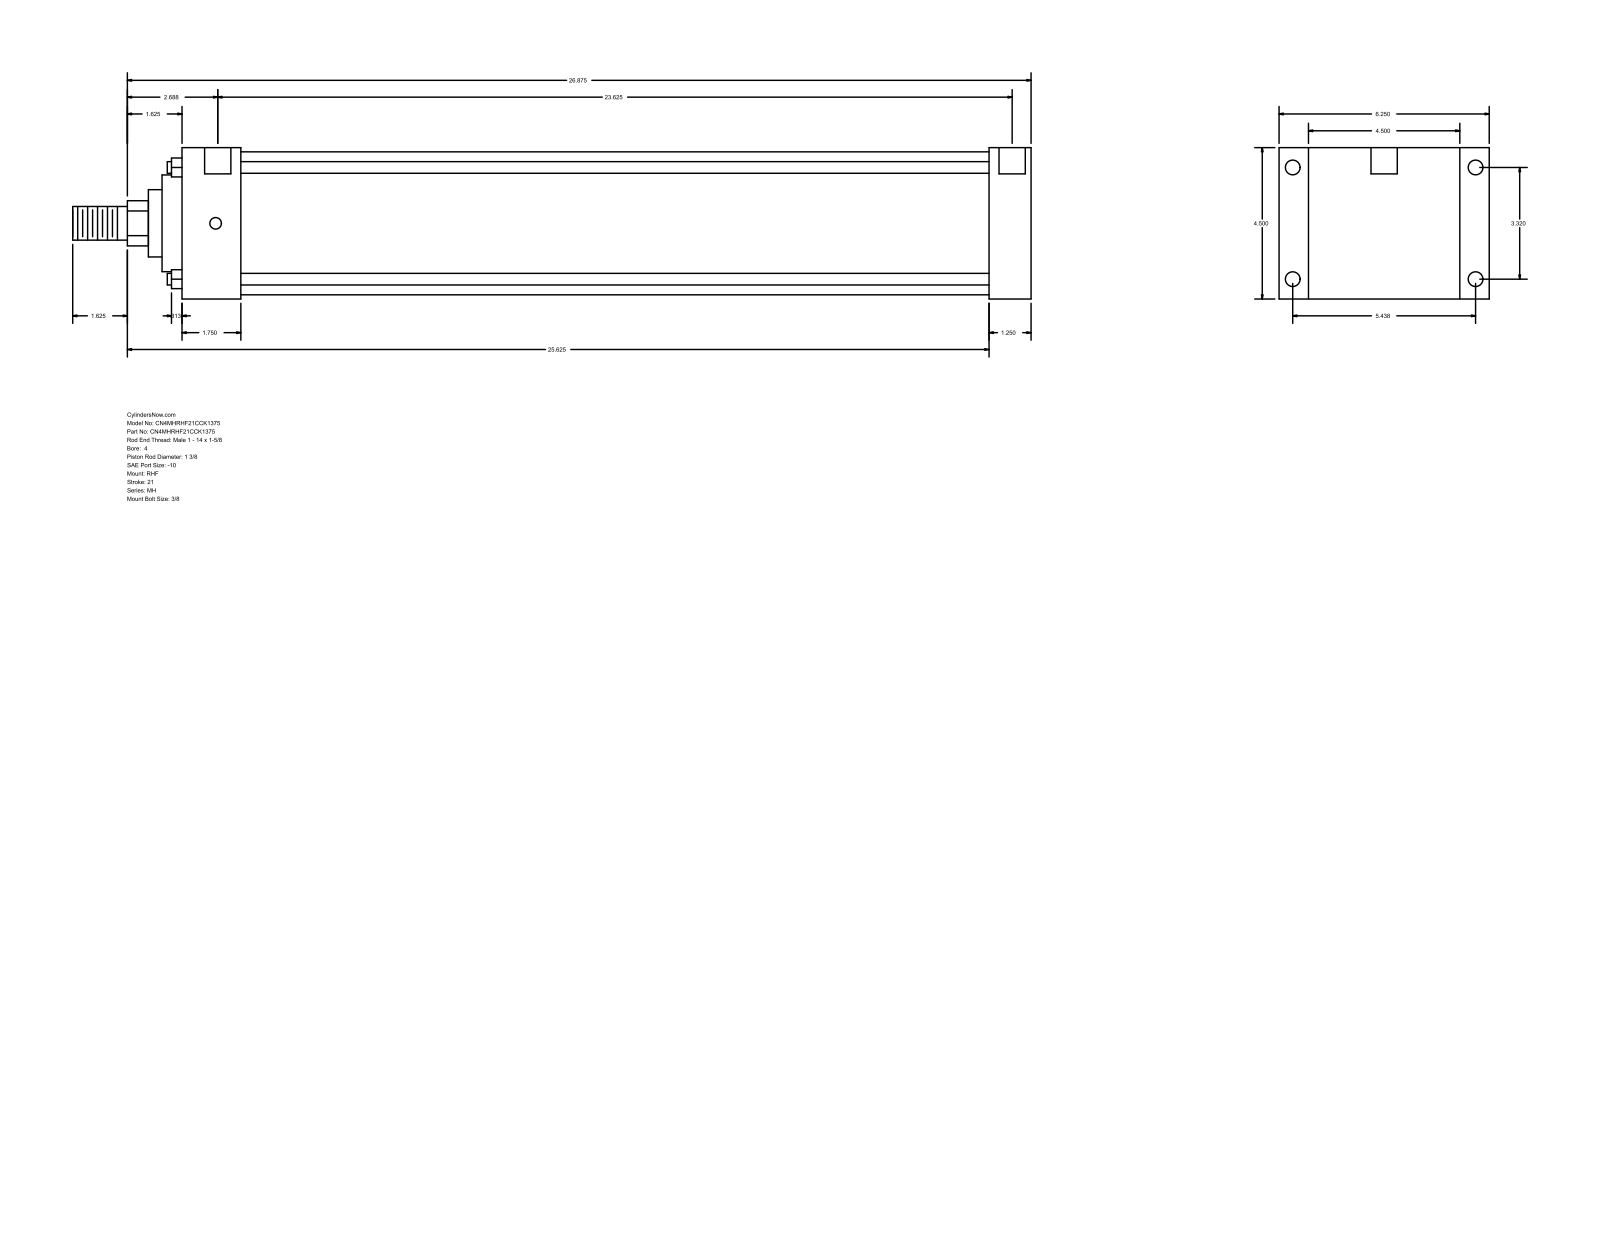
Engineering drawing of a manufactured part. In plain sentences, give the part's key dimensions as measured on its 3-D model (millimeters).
The part is named "MH_RHF__0400_1.375". Its 3-D file was written by "GSSL Pune (CONFIG_CONTROL_DESIGN)". It is 0 solids with 90 faces: 61 planar, 29 cylindrical and 0 other. Overall it measures 723.9 by 158.75 by 114.3 millimeters. Round holes: 4 of diameter 8.73, 4 of diameter 11.13, 2 of diameter 19.84. Round bosses or shafts: 4 of diameter 8.76, 1 of diameter 107.95, 1 of diameter 73.03, 1 of diameter 50.8, 1 of diameter 34.92, 1 of diameter 25.4. Partial cylindrical surfaces (rounded edges, fillets, slot ends): 1 of radius 17.06. The main face-to-face distances are 114.3, 31.74, 609.61, 641.35, 22.23, 136.53, 44.45, 565.16, 596.9, 158.76. The hole center spacings are 84.32, 138.12, 161.82, 603.25, 1.58, 1.59, 600.08, 601.66.
